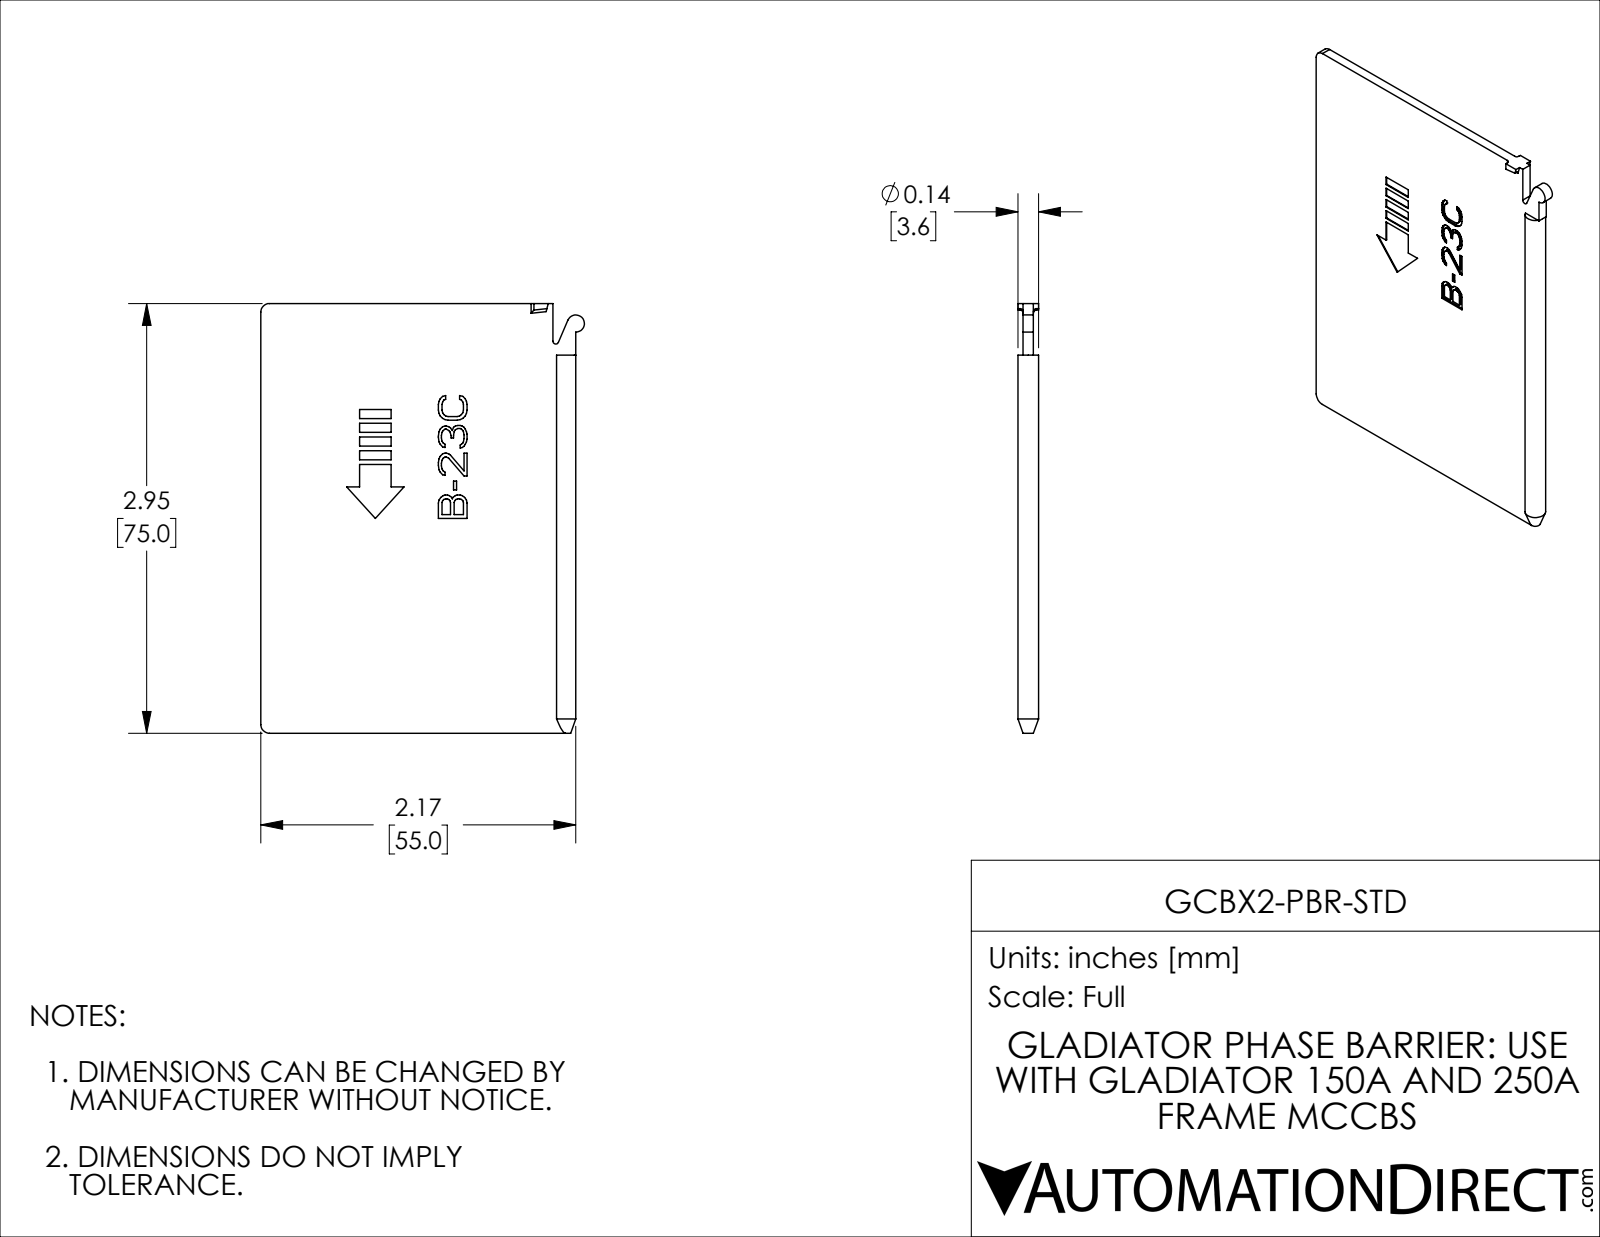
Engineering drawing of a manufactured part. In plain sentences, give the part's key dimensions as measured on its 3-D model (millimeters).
The part is named "GCBX2-PBR-STD". Its 3-D file was written by "SolidWorks 2021 (CONFIG_CONTROL_DESIGN)". It is 1 solid with 441 faces: 426 planar, 12 cylindrical and 3 other. Overall it measures 75 by 56.5 by 3.6 millimeters. Its volume is 7 600 cubic millimeters and its surface area 8 864 square millimeters. Round bosses or shafts: 1 of diameter 3.6. Partial cylindrical surfaces (rounded edges, fillets, slot ends): 5 of radius 0.5, 3 of radius 1.5. The main face-to-face distances are 1.8, 1.7, 1.5, 75, 1.3, 1.2, 2.4, 4, 51, 4.8.
